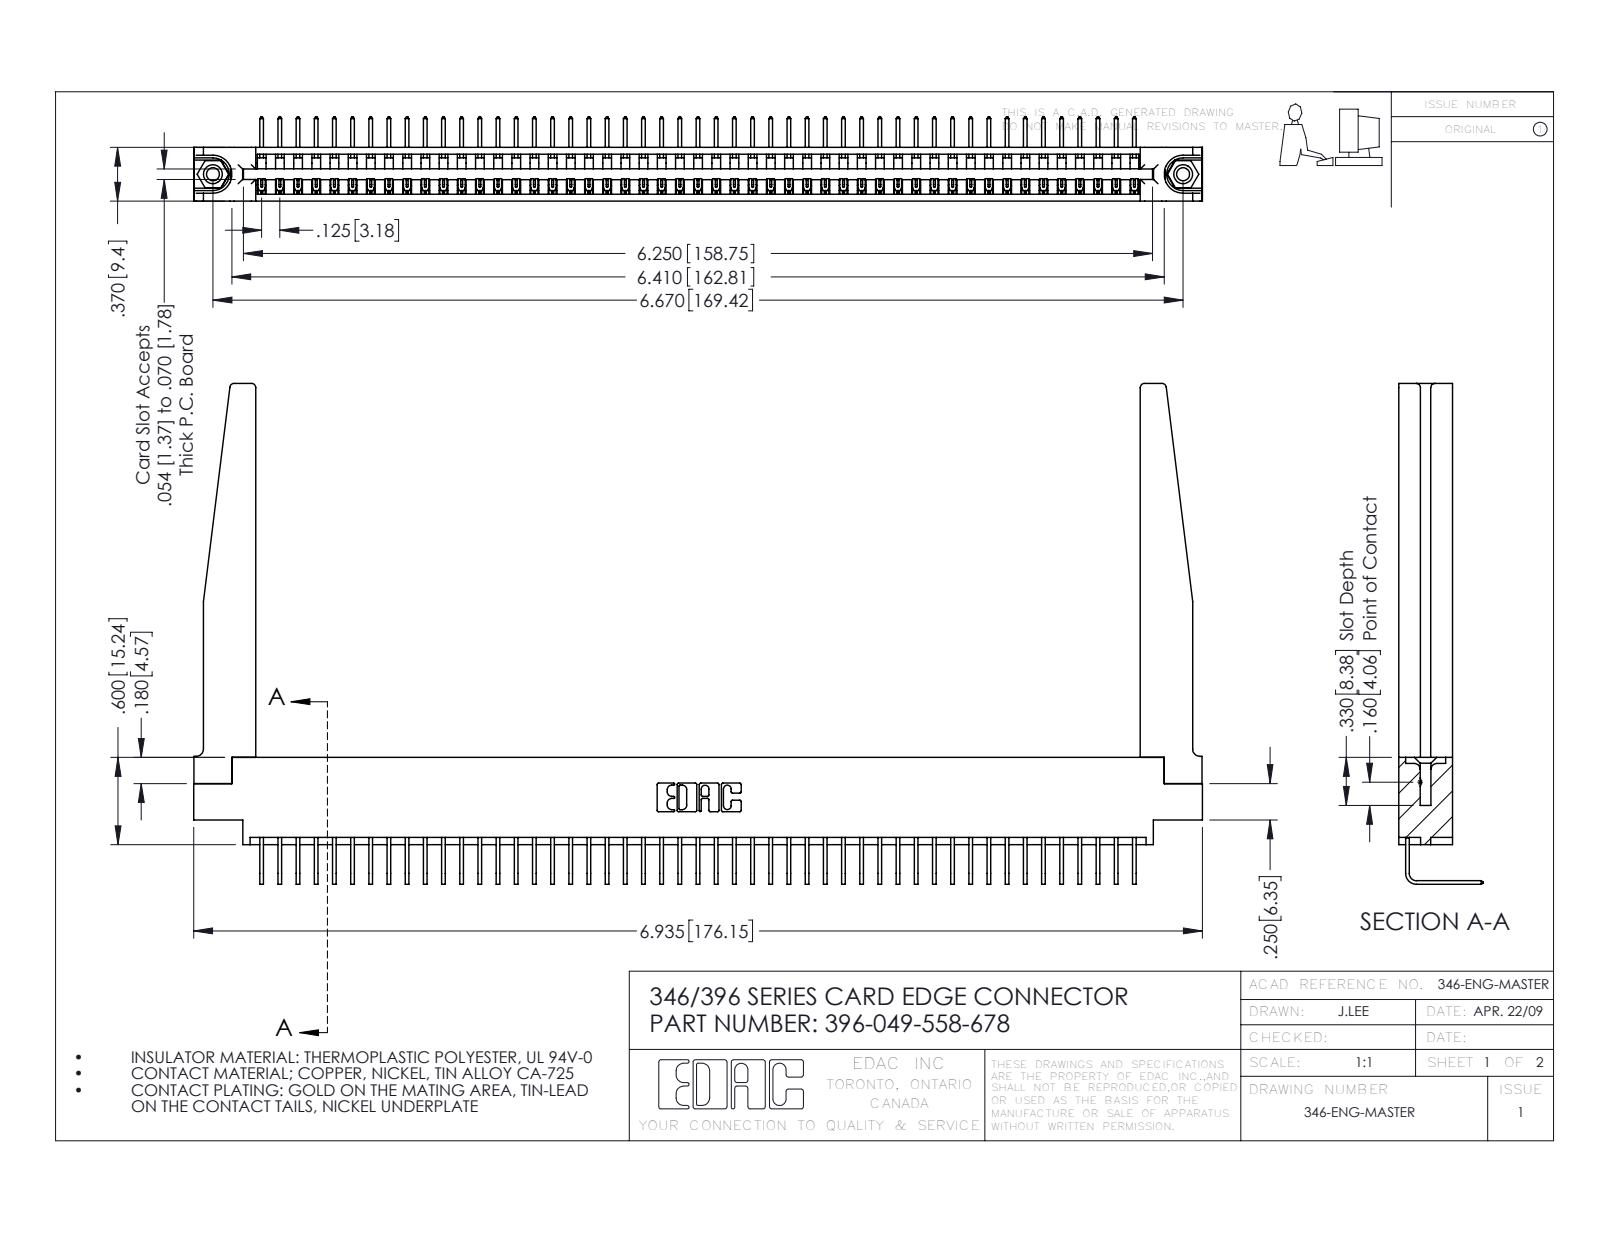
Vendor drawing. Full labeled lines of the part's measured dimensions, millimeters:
Part name (STEP PRODUCT): 396-049-558-678; 346-220-078_345-220-078; 345-250-001_345-250-001-102; 346 Part_0.170 Offset - 0.156 Dia-TH (+1 more)
STEP written by: SolidWorks 2016 (CONFIG_CONTROL_DESIGN)
Units: millimetres
Bodies: 54 solids, 3300 faces (2280 planar, 968 cylindrical, 52 other)
Overall size (bounding box): 176.1 × 87.5 × 14.7
Volume: 23 830 mm³ · Surface area: 28 900 mm²
Round holes (diameter × count): ⌀2.3 ×2, ⌀3.2 ×2, ⌀4 ×2, ⌀1.6 ×1
Round bosses / shafts (diameter × count): ⌀3.9 ×2
Partial cylindrical surfaces — rounded edges, fillets, slot ends (radius × count): R0.2 ×98, R0.3 ×22, R0.8 ×8, R0.2 ×6, R0.8 ×6, R0.7 ×3, R1.3 ×3, R0.8 ×2
Main face-to-face distances: 9.4, 8.2, 1.2, 1.8, 3.8, 7.6, 0.6, 6.4, 3.8, 5.6
Hole centre spacings: 6.2, 164.1, 169.4
